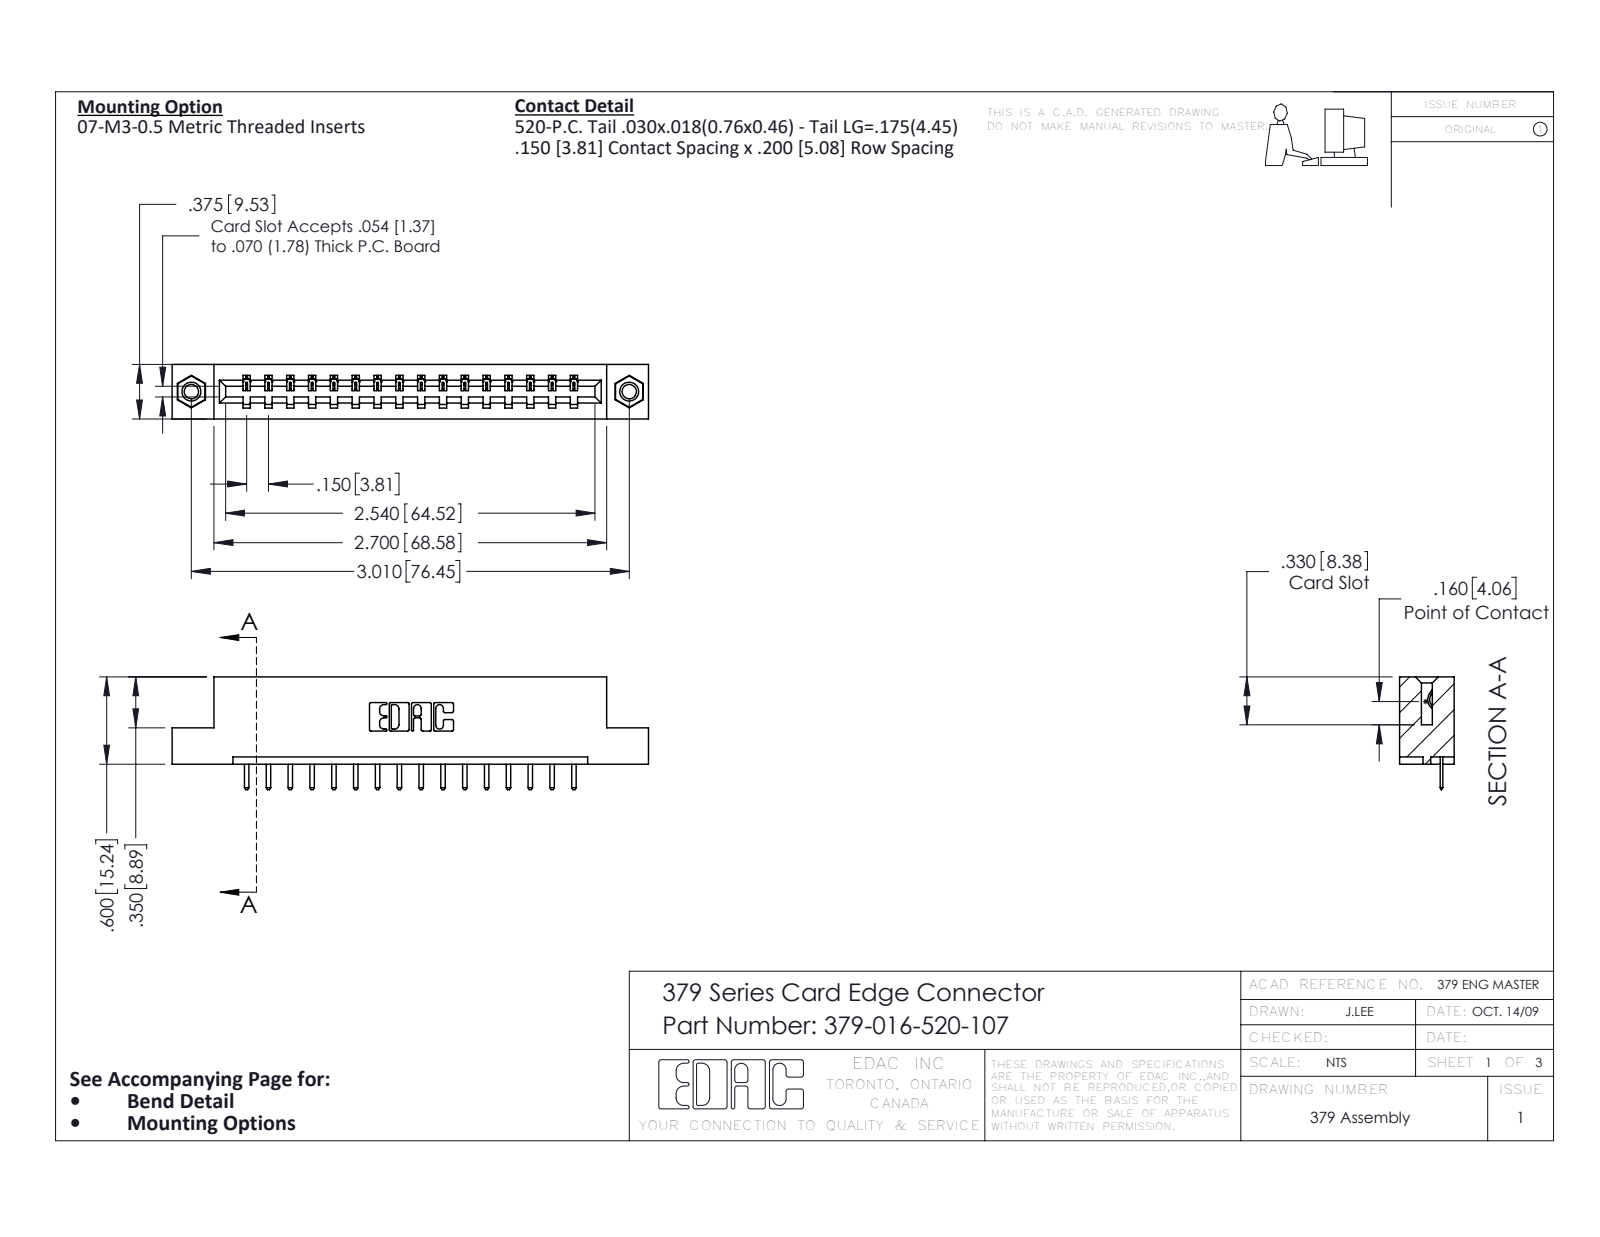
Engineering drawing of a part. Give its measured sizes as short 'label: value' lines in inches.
name: 345-292-001_345-293-120; 379-016-520-107; 379 Part_Flush - .156 Dia - TI; 345-250-001_345-250-005-103
written by: SolidWorks 2020 (CONFIG_CONTROL_DESIGN)
unit: in
bodies: 19 solids, 1166 faces (806 planar, 344 cylindrical, 16 other)
size: 3.275 × 0.775 × 0.375
volume: 0.511 in³; area: 12.88 in²
holes: 2× ⌀0.098, 2× ⌀0.125, 2× ⌀0.156
bosses: 2× ⌀0.155
rounds: 34× R0.01, 32× R0.006, 22× R0.01, 6× R0.007, 6× R0.031, 3× R0.026, 1× R0.014, 1× R0.022
face distances: 0.3, 0.375, 0.075, 0.6, 0.15, 0.225, 0.45, 0.75, 0.2, 0.9
hole spacings: 3.01
